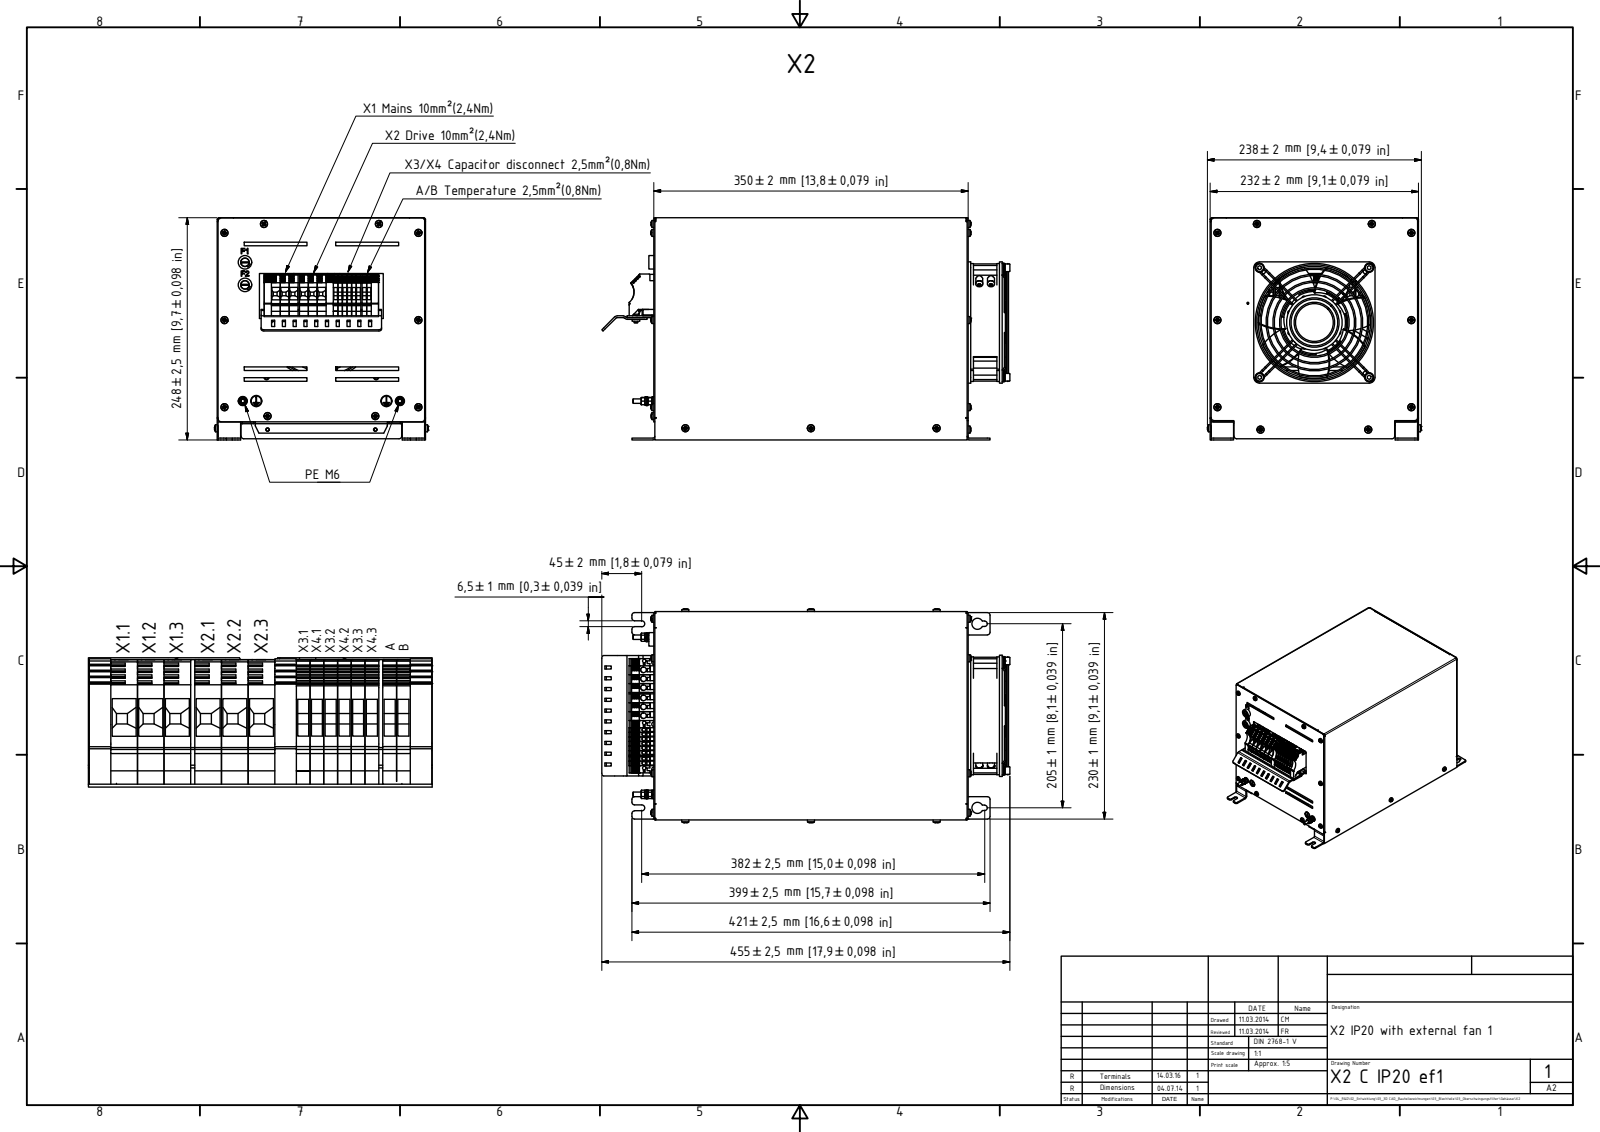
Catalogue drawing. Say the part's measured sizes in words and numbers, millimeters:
The part is named "10100277 Bodenblech X2; 10100385 Deckel X2-A; 10100459 Lüfterblech X2-A; 10100384 Anschlussblech X2-A (+8 more)". Its 3-D file was written by "Autodesk Inventor 2015 (AUTOMOTIVE_DESIGN)". It is 108 solids with 8238 faces: 5175 planar, 2115 cylindrical and 948 other. Overall it measures 454.54 by 247.5 by 238.23 millimeters. Its volume is 949 578 cubic millimeters and its surface area 1 223 000 square millimeters. Round holes: 19 of diameter 4, 17 of diameter 3.24, 15 of diameter 5, 12 of diameter 6.32, 10 of diameter 6, 10 of diameter 6.5, 8 of diameter 3.5, 7 of diameter 4.2, 6 of diameter 5.3, 6 of diameter 5.4, 4 of diameter 5.5, 4 of diameter 12.5. Round bosses or shafts: 24 of diameter 1.5, 22 of diameter 4, 16 of diameter 3.65, 8 of diameter 9.2, 6 of diameter 10, 6 of diameter 8.5, 6 of diameter 5, 4 of diameter 7.74. Partial cylindrical surfaces (rounded edges, fillets, slot ends): 59 of radius 0.5, 46 of radius 2, 44 of radius 0.15, 36 of radius 0.75, 35 of radius 0.1, 33 of radius 3, 25 of radius 2.5, 24 of radius 0.45. The main face-to-face distances are 1, 231, 2, 349, 230, 232, 348, 228.5, 229.5, 226.5. The hole center spacings are 117.73, 15, 35, 86.27, 97, 122, 150.85, 210.
